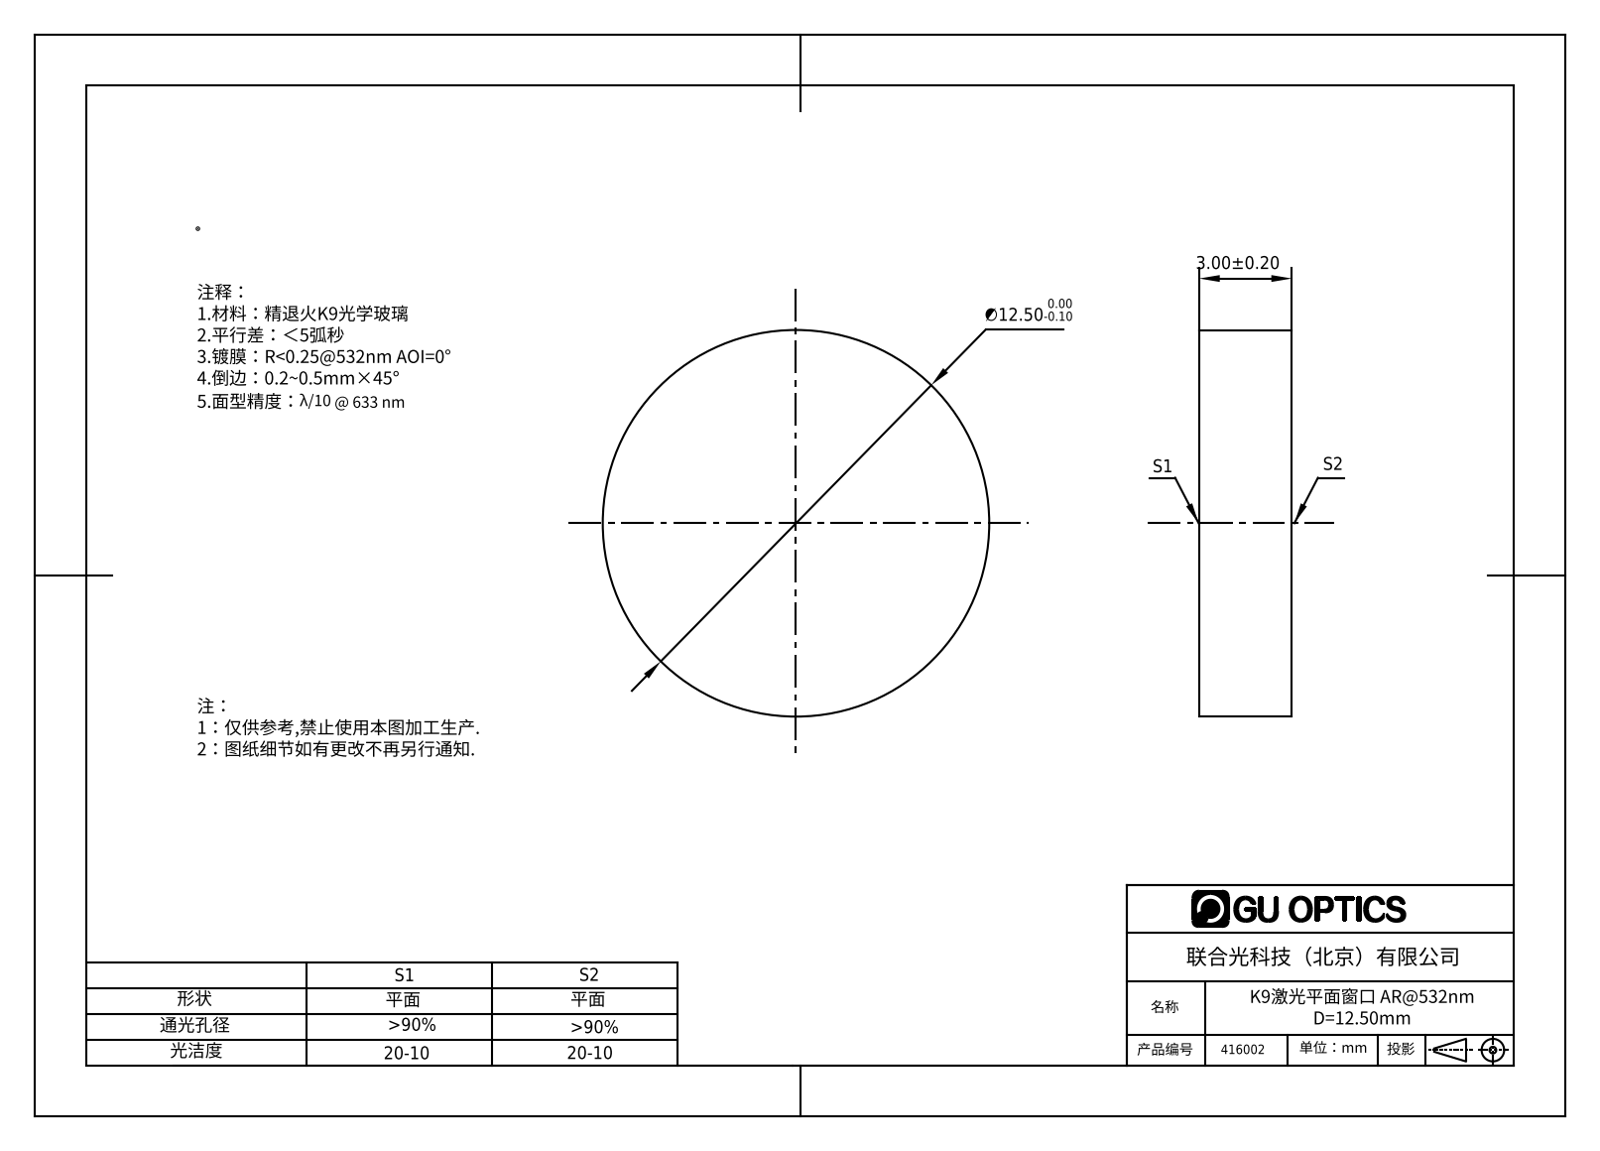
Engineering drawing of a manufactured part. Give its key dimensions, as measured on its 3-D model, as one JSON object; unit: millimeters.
{"part_name": "416002", "step_written_by": "SolidWorks 2016 (CONFIG_CONTROL_DESIGN)", "units": "millimeters", "bodies": {"solids": 1, "faces": 4, "planar": 2, "cylindrical": 2, "other": 0}, "overall_size": [12.5, 12.5, 3], "volume_mm3": 368, "surface_area_mm2": 363, "round_bosses_or_shafts": [[12.5, 1]], "face_to_face_distances": [3]}
